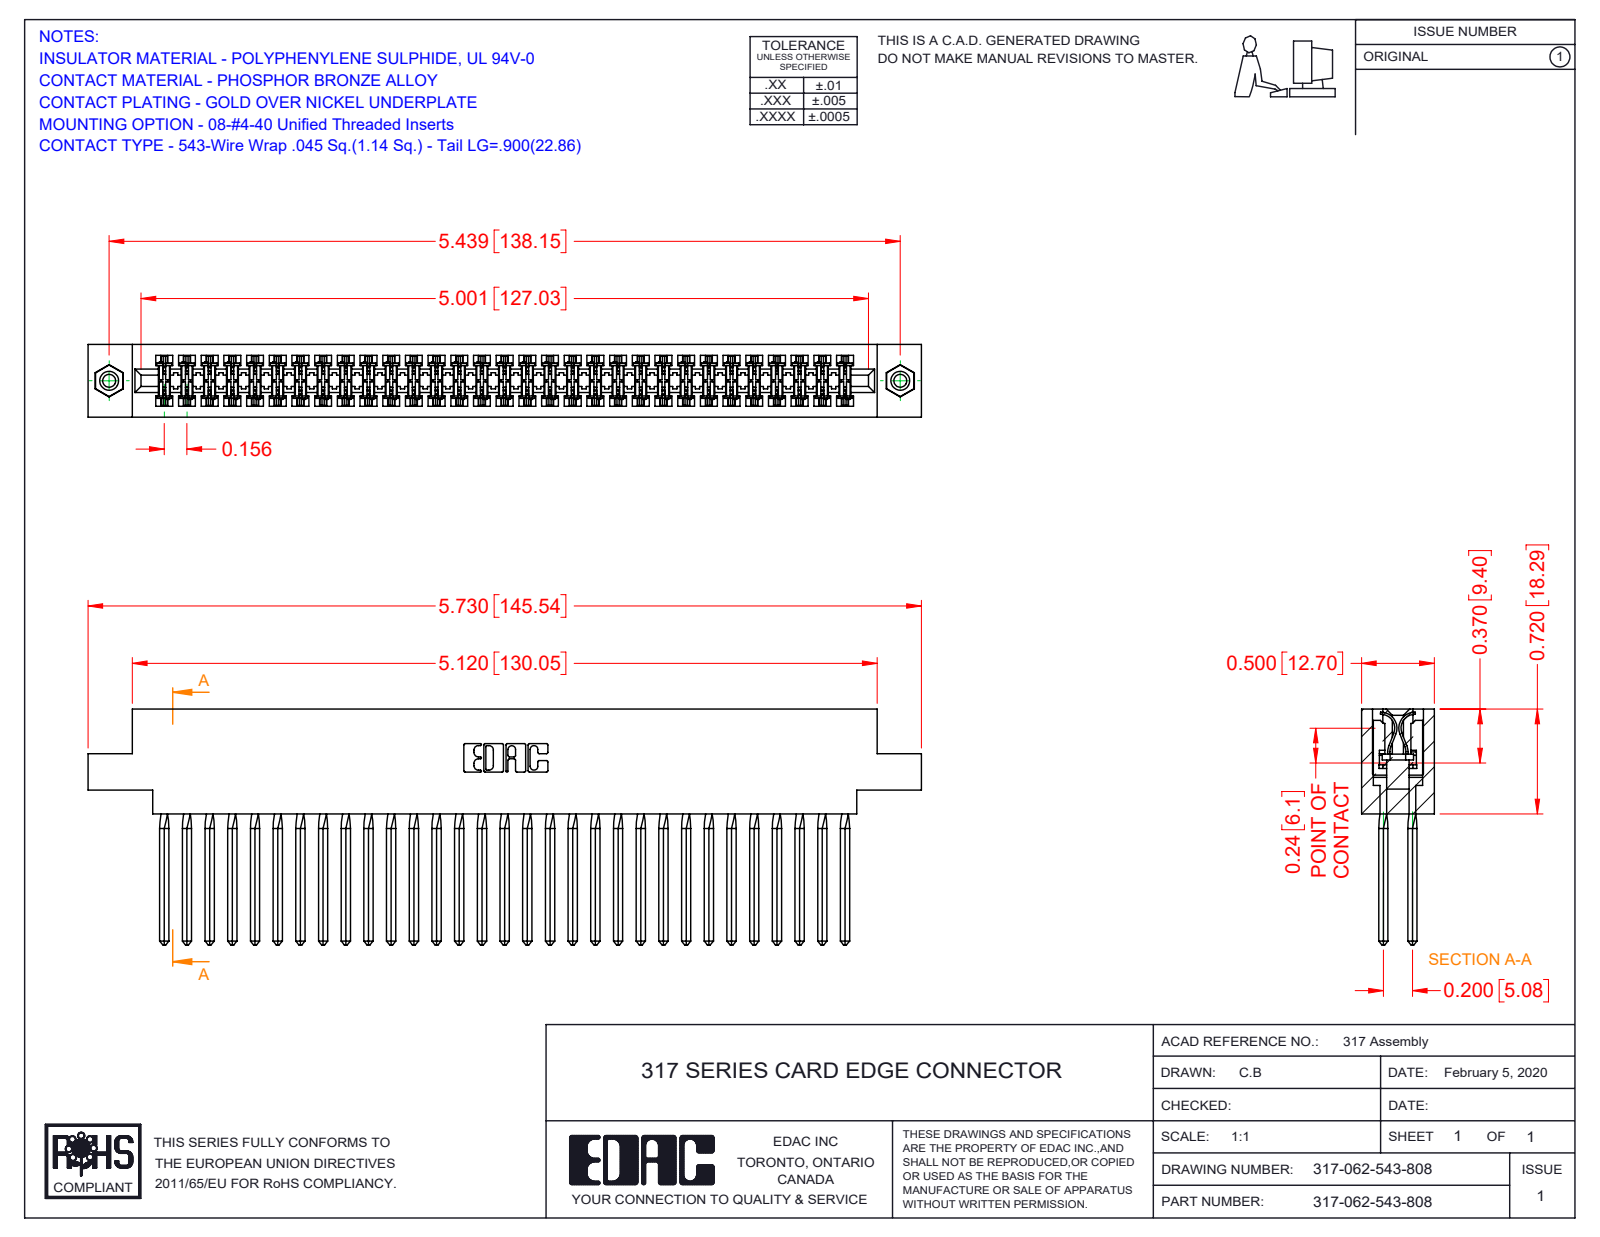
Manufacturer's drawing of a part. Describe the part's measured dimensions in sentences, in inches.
The part is named "317-290-001_543; 345-250-001_345-250-003-102; 317-062-543-808; 317 Part_.156 Dia - TI". Its 3-D file was written by "SolidWorks 2016 (CONFIG_CONTROL_DESIGN)". It is 65 solids with 5680 faces: 4616 planar, 800 cylindrical and 264 other. Overall it measures 5.73 by 1.62 by 0.5 inches. Its volume is 1.486 cubic inches and its surface area 56.64 square inches. Round holes: 2 of diameter 0.089, 2 of diameter 0.125, 2 of diameter 0.156. Round bosses or shafts: 2 of diameter 0.155. Partial cylindrical surfaces (rounded edges, fillets, slot ends): 124 of radius 0.015, 22 of radius 0.01, 6 of radius 0.007, 6 of radius 0.031, 3 of radius 0.026, 2 of radius 0.095, 2 of radius 0.1, 2 of radius 0.11. The main face-to-face distances are 0.5, 0.075, 0.425, 0.35, 0.11, 0.195, 0.094, 0.2, 0.115, 0.131. The hole center spacings are 5.439.
